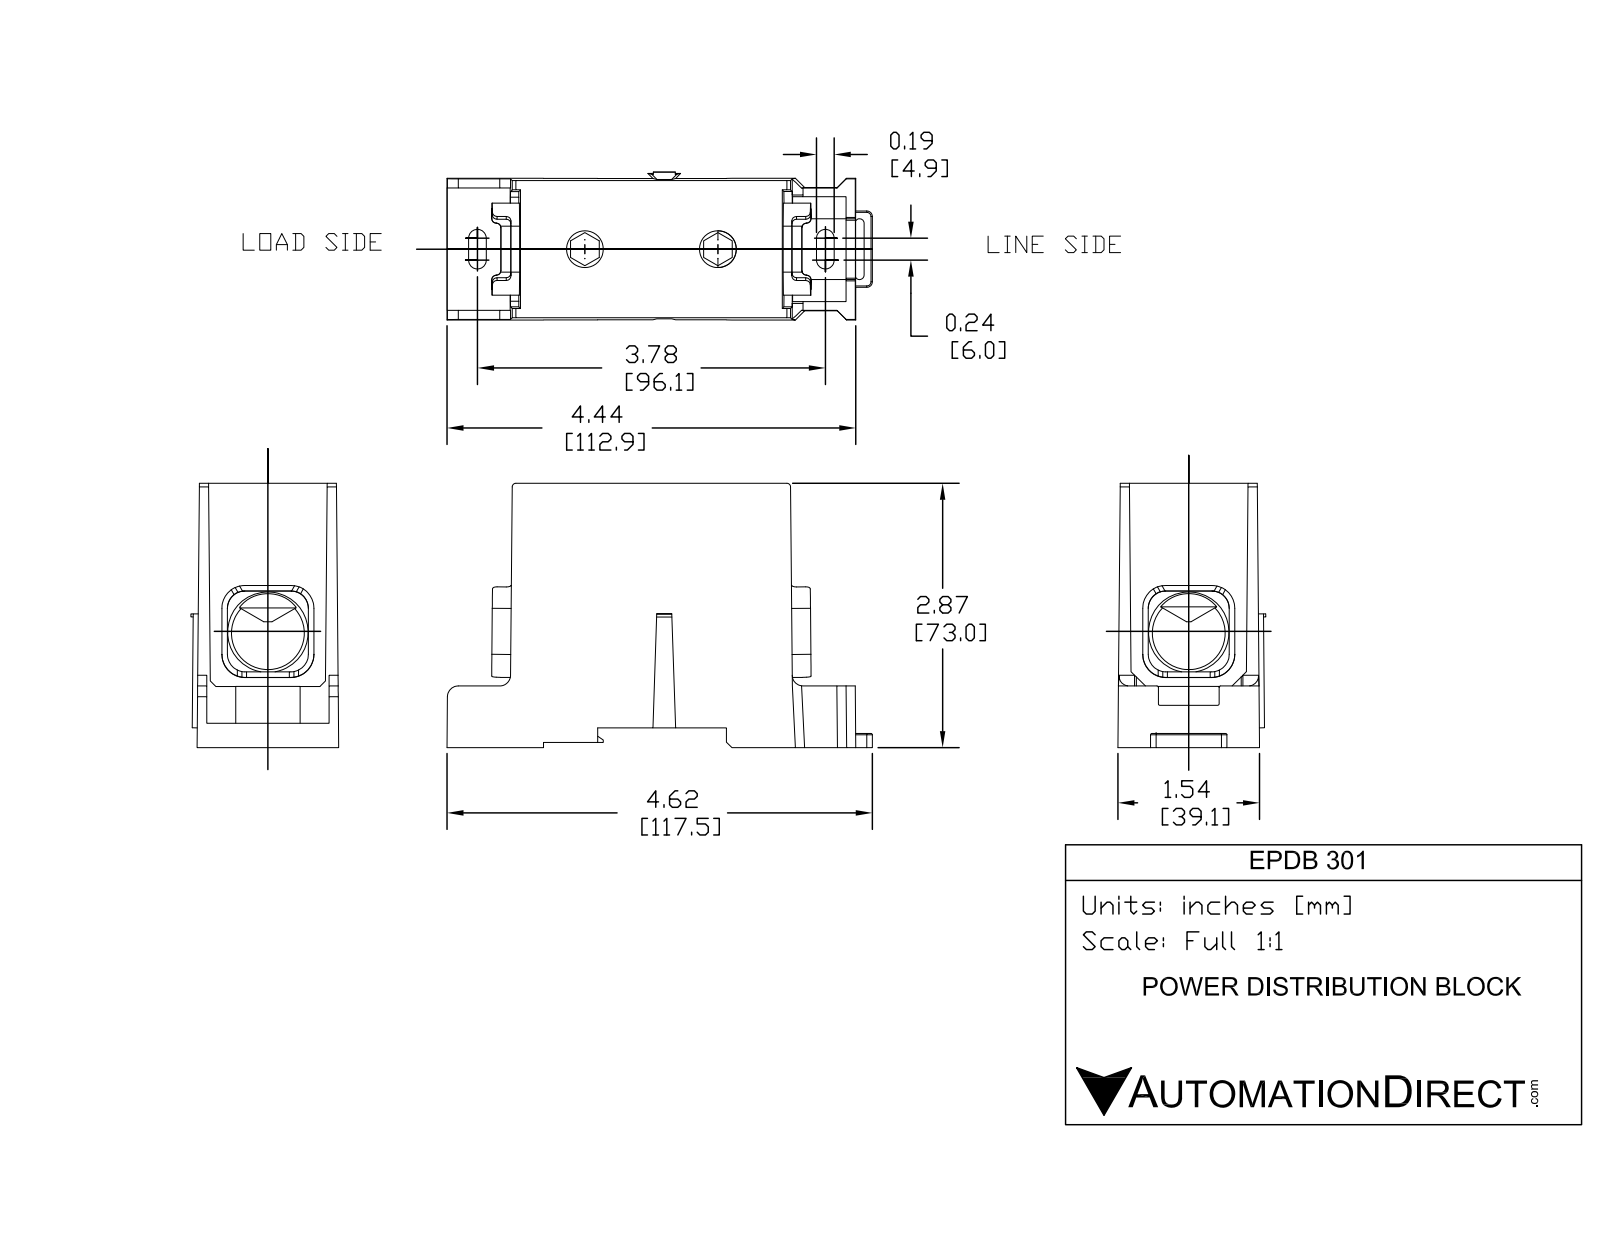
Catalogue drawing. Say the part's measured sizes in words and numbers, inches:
The part is named "EPDB301". Its 3-D file was written by "SolidWorks 2011 (CONFIG_CONTROL_DESIGN)". It is 1 solid with 238 faces: 151 planar, 75 cylindrical and 12 other. Overall it measures 4.625 by 2.874 by 1.608 inches. Its volume is 11.7 cubic inches and its surface area 57 square inches. Round holes: 2 of diameter 0.4. Round bosses or shafts: 2 of diameter 0.609. Partial cylindrical surfaces (rounded edges, fillets, slot ends): 16 of radius 0.05, 8 of radius 0.19, 8 of radius 0.25, 7 of radius 0.015, 4 of radius 0.096, 3 of radius 0.118, 2 of radius 0.04, 2 of radius 0.049. The main face-to-face distances are 2.874, 0.216, 2.658, 0.06, 0.09, 0.774, 0.683, 1.195, 1.285, 1.969. The hole center spacings are 1.446.
